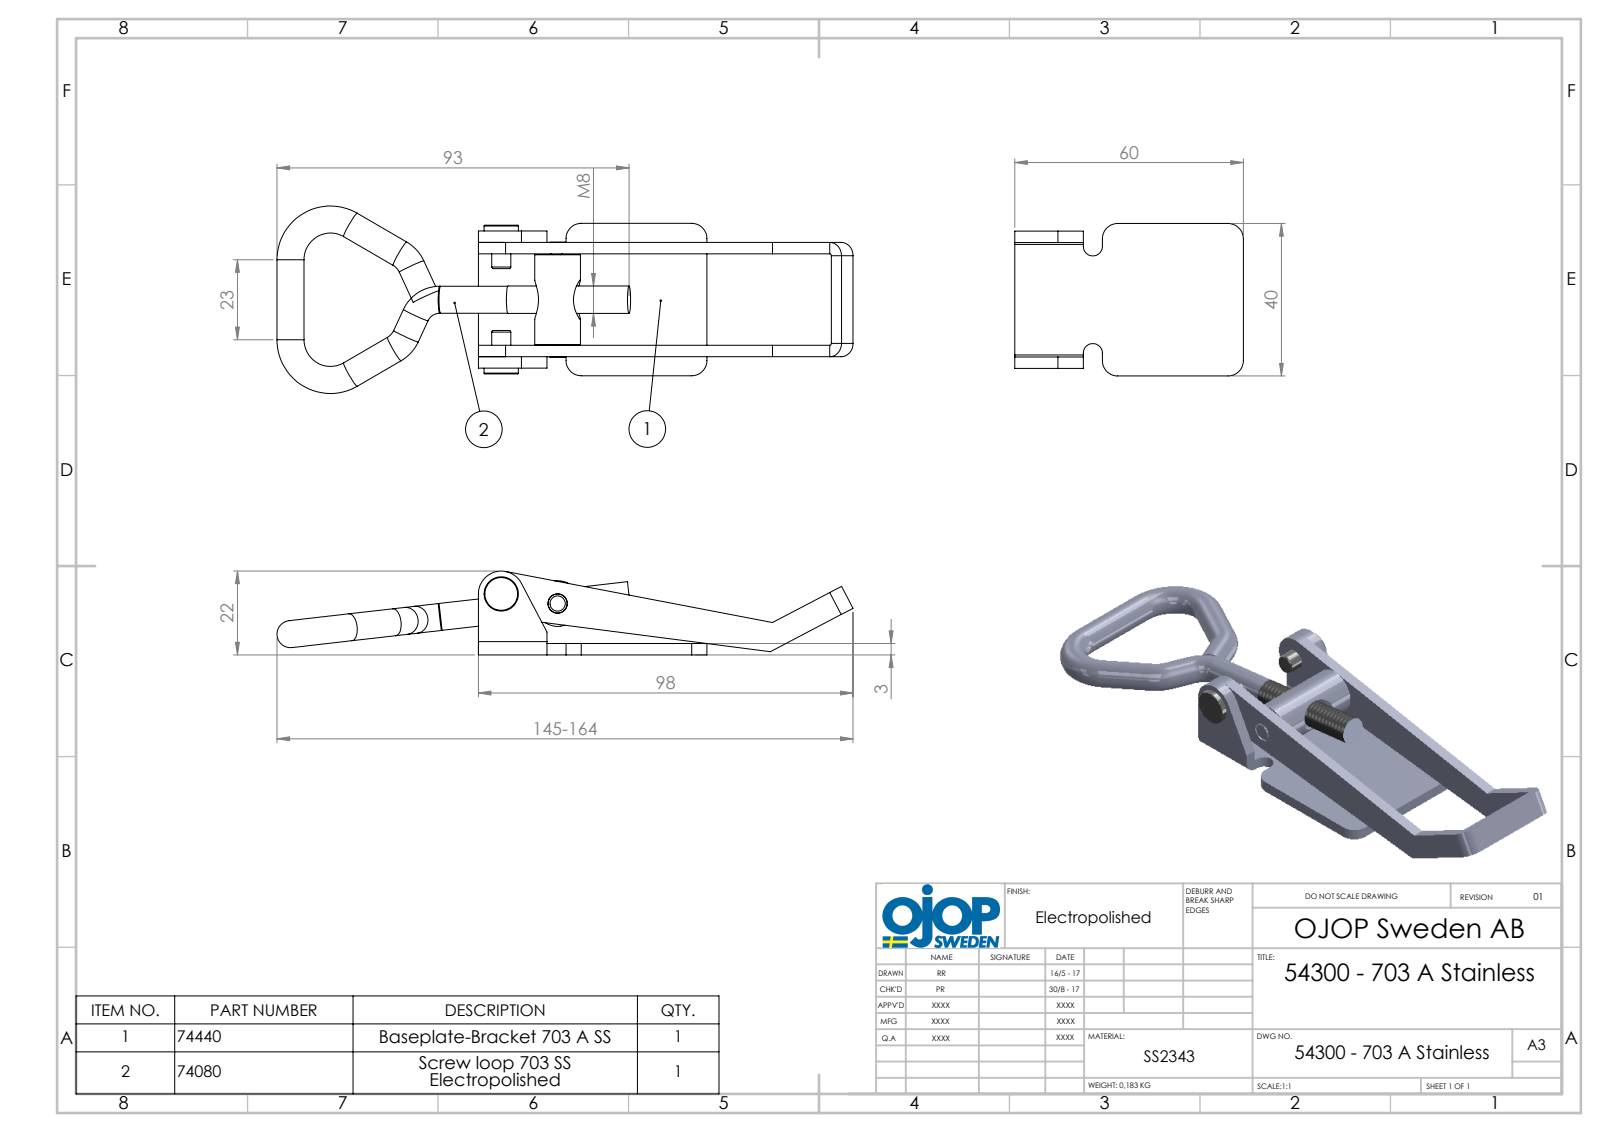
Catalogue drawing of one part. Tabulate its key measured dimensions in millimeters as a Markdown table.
| quantity | value |
| --- | --- |
| part name | 703 - Platta A RF; 54300 - 703 A Stainless; 703 - Skruvögla; 704 - Rivet Gradin (+2 more) |
| STEP written by | SolidWorks 2015 (AUTOMOTIVE_DESIGN) |
| units | millimeters |
| bodies | 6 solids, 148 faces (58 planar, 60 cylindrical, 30 other) |
| overall size | 159.17 × 49.4 × 22 |
| volume | 23 842 mm³ |
| surface area | 17 697 mm² |
| round holes (diameter × count) | 5.1 × 2, 7.2 × 2 |
| round bosses / shafts (diameter × count) | 7 × 4, 5 × 2, 12 × 1, 9 × 1, 7.7 × 1 |
| partial cylindrical surfaces (radius × count) | 4 × 6, 0.5 × 2, 1 × 2, 2.5 × 2, 3.5 × 2, 6 × 1 |
| main face-to-face distances | 3, 27, 30, 24, 6, 33, 36, 6.2, 29.8, 3.2 |
| hole center spacings | 15.01 |
